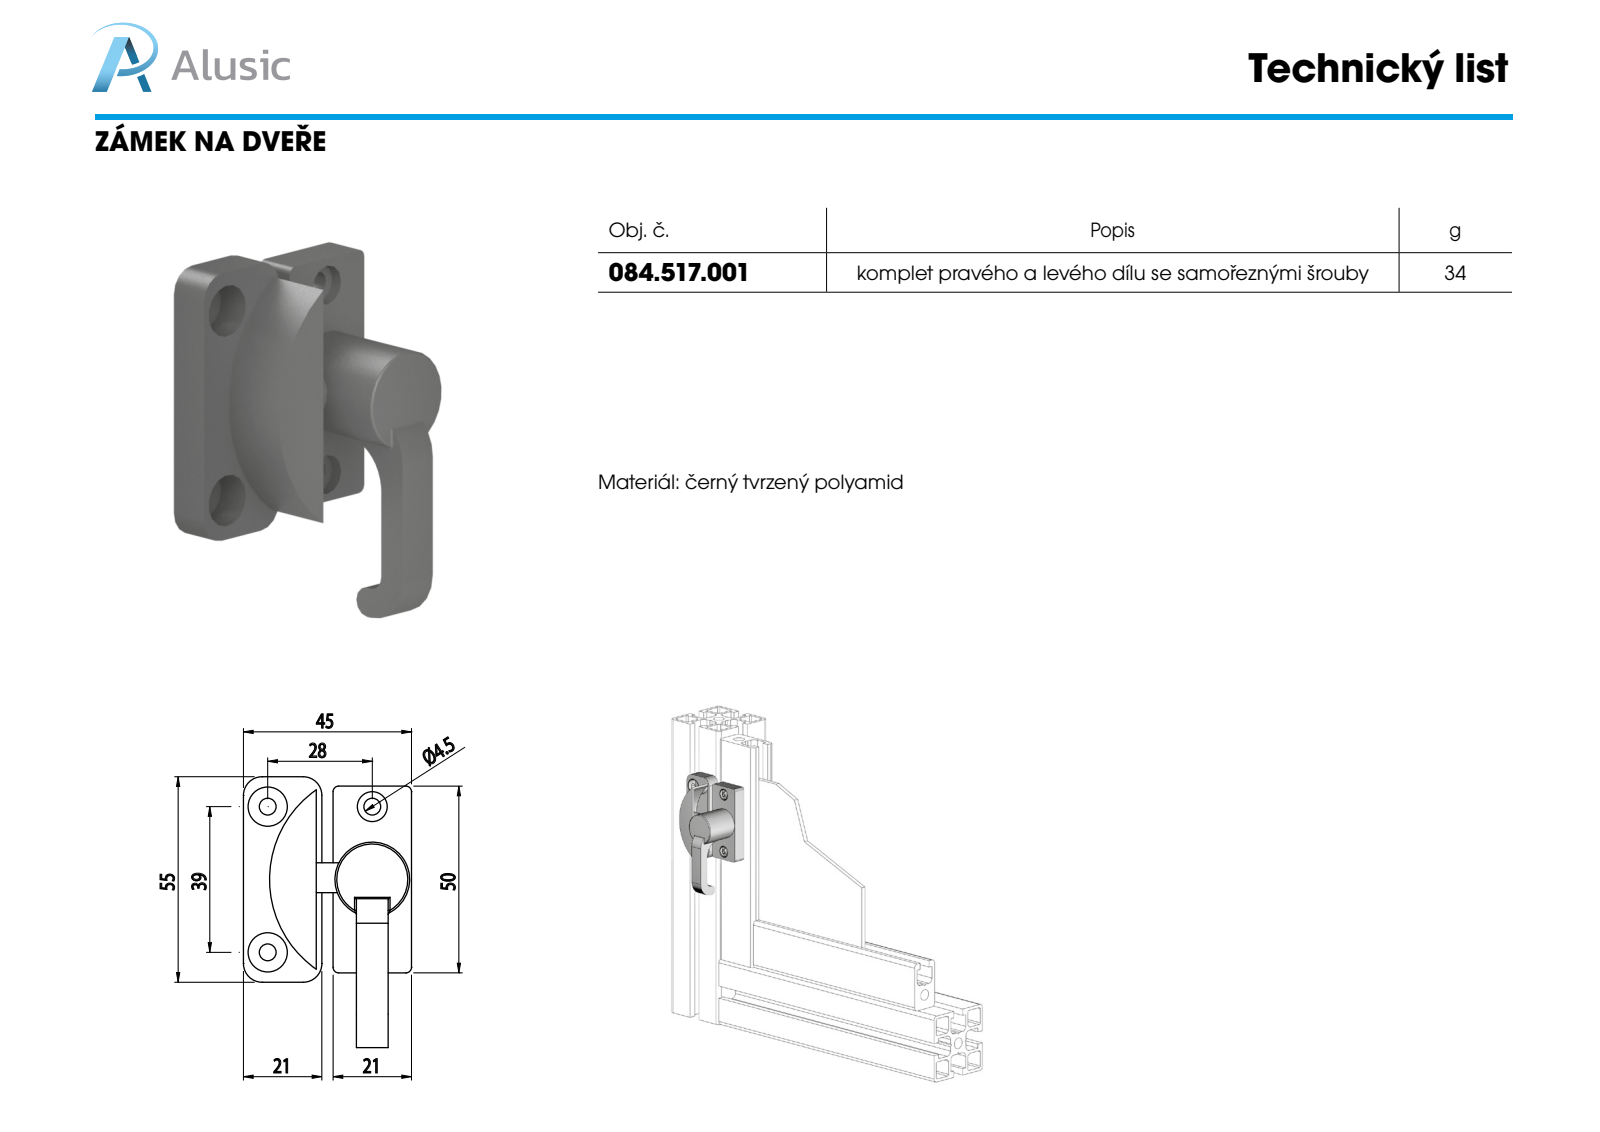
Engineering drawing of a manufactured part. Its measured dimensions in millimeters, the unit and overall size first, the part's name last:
Units: millimetres
Overall size (bounding box): 72.5 × 45 × 34
Round holes (diameter × count): ⌀4.5 ×4, ⌀8 ×2, ⌀10.5 ×2
Round bosses / shafts (diameter × count): ⌀12.5 ×2, ⌀20 ×1, ⌀8 ×1
Partial cylindrical surfaces — rounded edges, fillets, slot ends (radius × count): R0.5 ×5, R1.5 ×4, R4 ×4, R5 ×4, R3 ×2, R9 ×2, R28.29 ×1, R29.29 ×1
Main face-to-face distances: 1, 8.5, 7.5, 21, 14, 21.5, 24, 3, 22.5, 20
Hole centre spacings: 28, 39, 48.01
Volume: 22 961 mm³ · Surface area: 14 908 mm²
Bodies: 2 solids, 93 faces (36 planar, 50 cylindrical, 7 other)
Part name (STEP PRODUCT): 084.517.001
STEP written by: SolidWorks 2011 (CONFIG_CONTROL_DESIGN)
